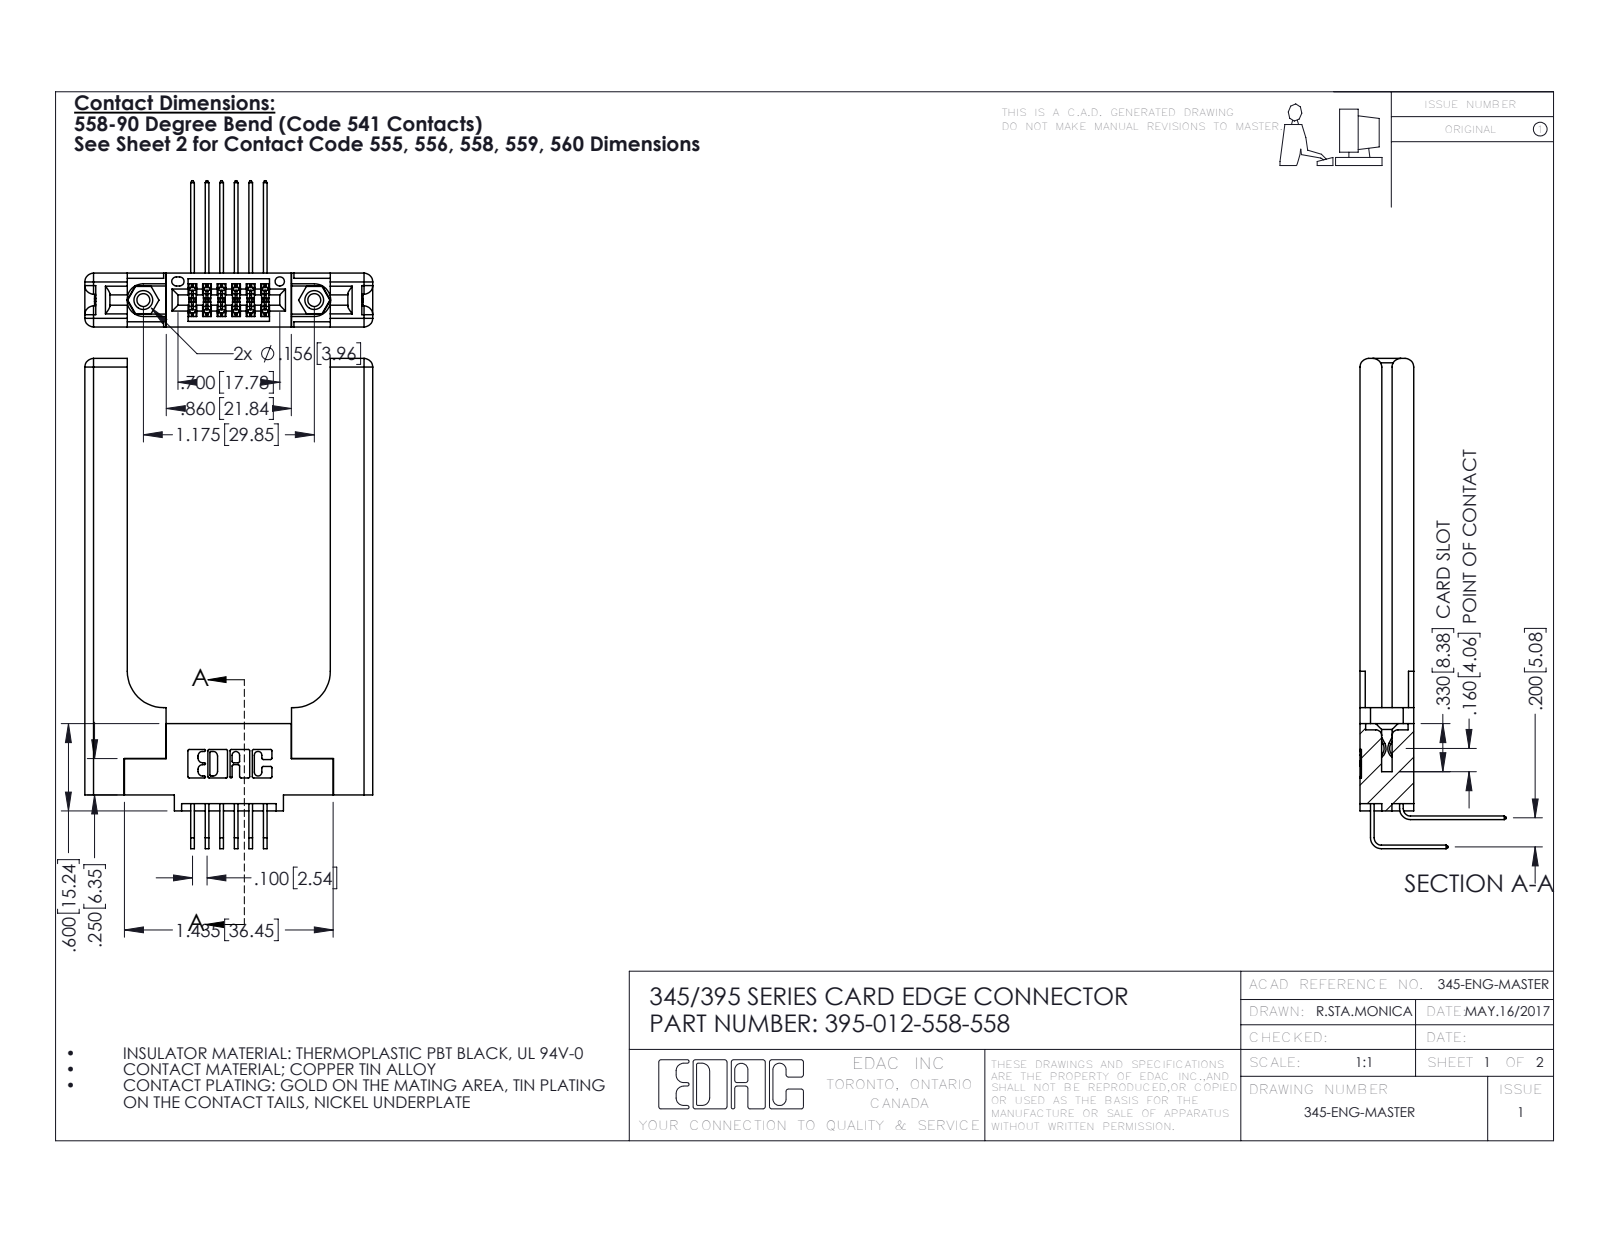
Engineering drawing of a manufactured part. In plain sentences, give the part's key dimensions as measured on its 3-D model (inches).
The part is named "345-220-058_345-220-058; 345-292-001_558 Tail - 2; 345-250-001_345-250-001-102; 395-012-558-558 (+2 more)". Its 3-D file was written by "SolidWorks 2016 (CONFIG_CONTROL_DESIGN)". It is 17 solids with 1010 faces: 652 planar, 298 cylindrical and 60 other. Overall it measures 3.369 by 1.979 by 1.005 inches. Its volume is 0.795 cubic inches and its surface area 17.82 square inches. Round holes: 2 of diameter 0.089, 2 of diameter 0.125, 2 of diameter 0.156, 1 of diameter 0.064. Round bosses or shafts: 2 of diameter 0.155. Partial cylindrical surfaces (rounded edges, fillets, slot ends): 22 of radius 0.01, 19 of radius 0.006, 16 of radius 0.06, 6 of radius 0.007, 6 of radius 0.031, 3 of radius 0.026, 2 of radius 0.014, 2 of radius 0.019. The main face-to-face distances are 0.37, 0.15, 0.22, 0.072, 0.077, 0.148, 0.298, 1.396, 0.071, 0.292. The hole center spacings are 0.27, 0.946, 1.175.
